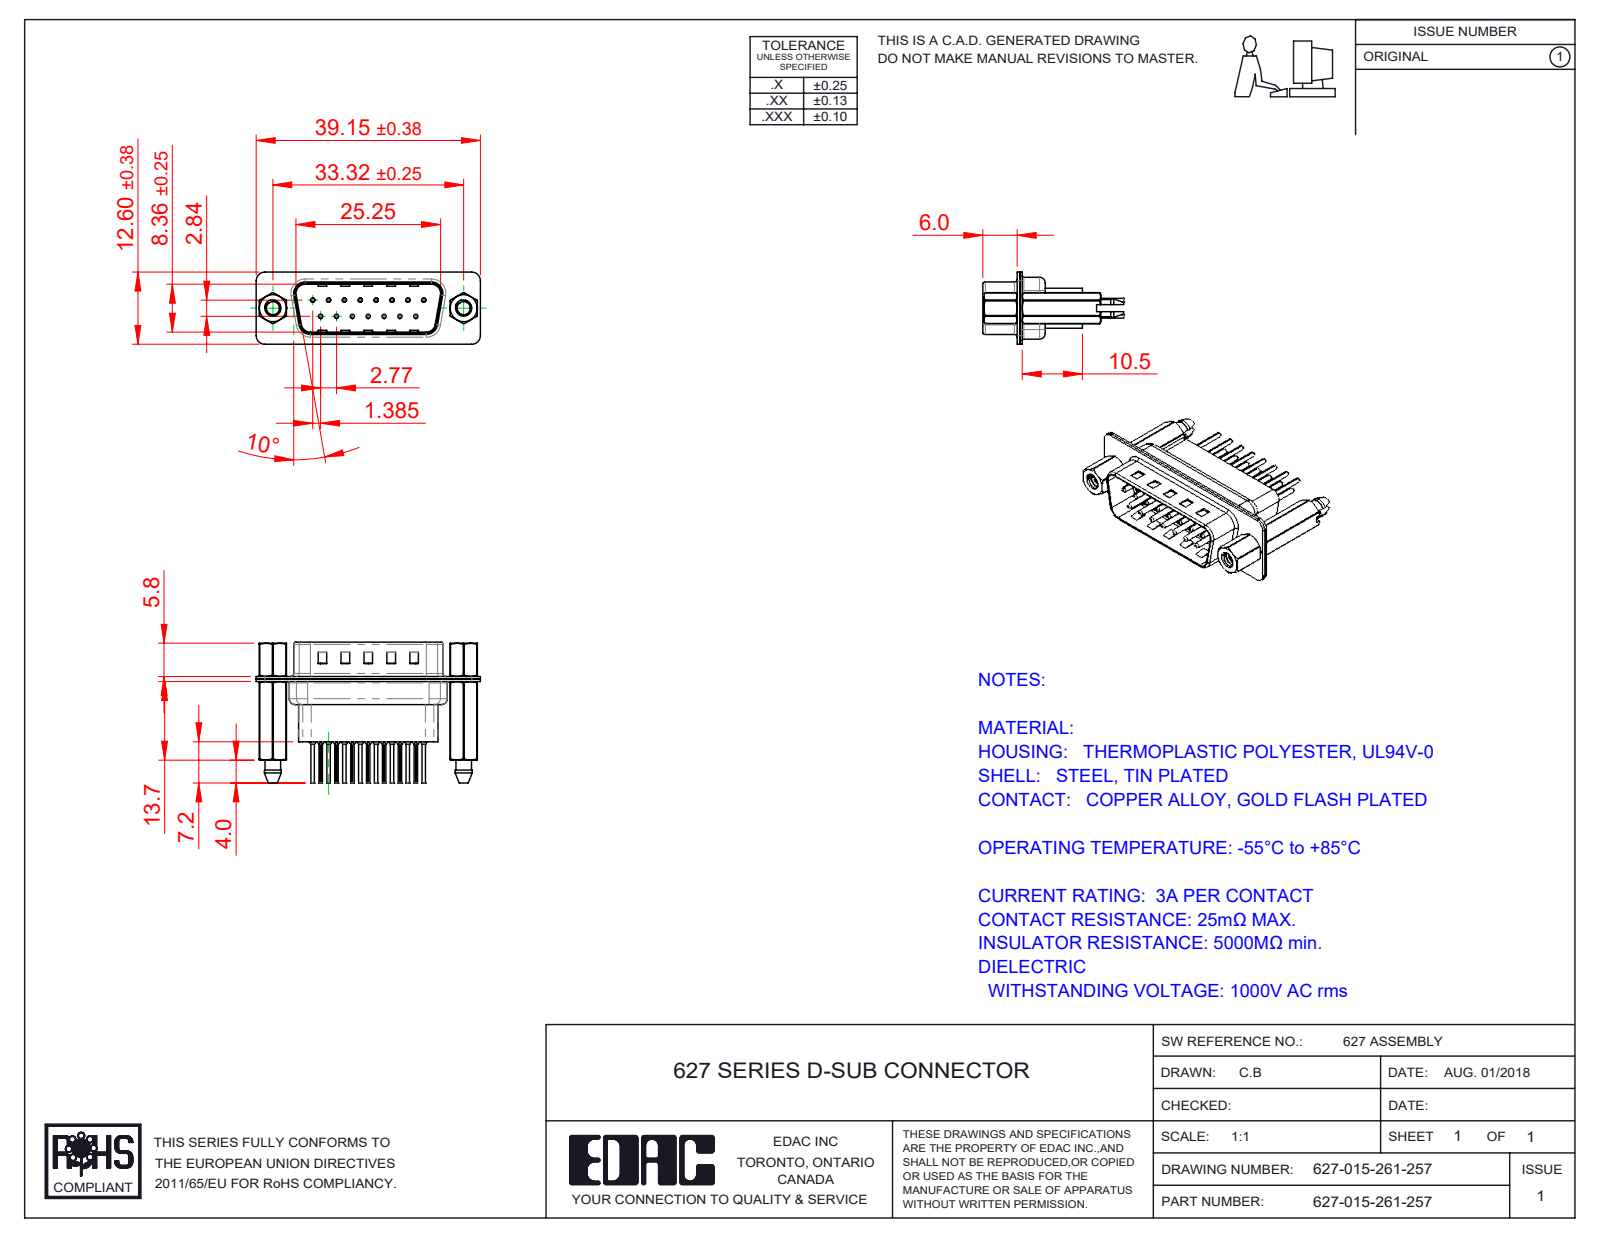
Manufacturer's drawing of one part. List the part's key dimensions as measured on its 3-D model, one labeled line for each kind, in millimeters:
Part name (STEP PRODUCT): 627 Housing_15 HP; 627 Shell Rear_15 Contacts; 627-015-261-057; 627 Contact Row 1_61 (+4 more)
STEP written by: SolidWorks 2020 (CONFIG_CONTROL_DESIGN)
Units: millimetres
Bodies: 22 solids, 2044 faces (553 planar, 826 cylindrical, 665 other)
Overall size (bounding box): 39.15 × 24.6 × 12.6
Volume: 3 108 mm³ · Surface area: 7 977 mm²
Round holes (diameter × count): ⌀0.2 ×15, ⌀0.35 ×15, ⌀1.1 ×15, ⌀1.6 ×15, ⌀2.26 ×2, ⌀2.29 ×2, ⌀4 ×2, ⌀4.8 ×2
Round bosses / shafts (diameter × count): ⌀2 ×15, ⌀1.5 ×15, ⌀0.75 ×15, ⌀0.6 ×15, ⌀4.9 ×2, ⌀2.79 ×2
Partial cylindrical surfaces — rounded edges, fillets, slot ends (radius × count): R0.1 ×30, R1.5 ×18, R2 ×12, R1.6 ×10, R0.5 ×8, R0.25 ×4, R0.6 ×4, R0.65 ×4
Main face-to-face distances: 0.4, 0.45, 4.76, 0.9, 0.82, 9.58, 1.5, 0.68, 7.68, 16.66
Hole centre spacings: 3.16, 2.77, 5.54, 8.31, 11.08, 5.03, 5.04, 7.48
